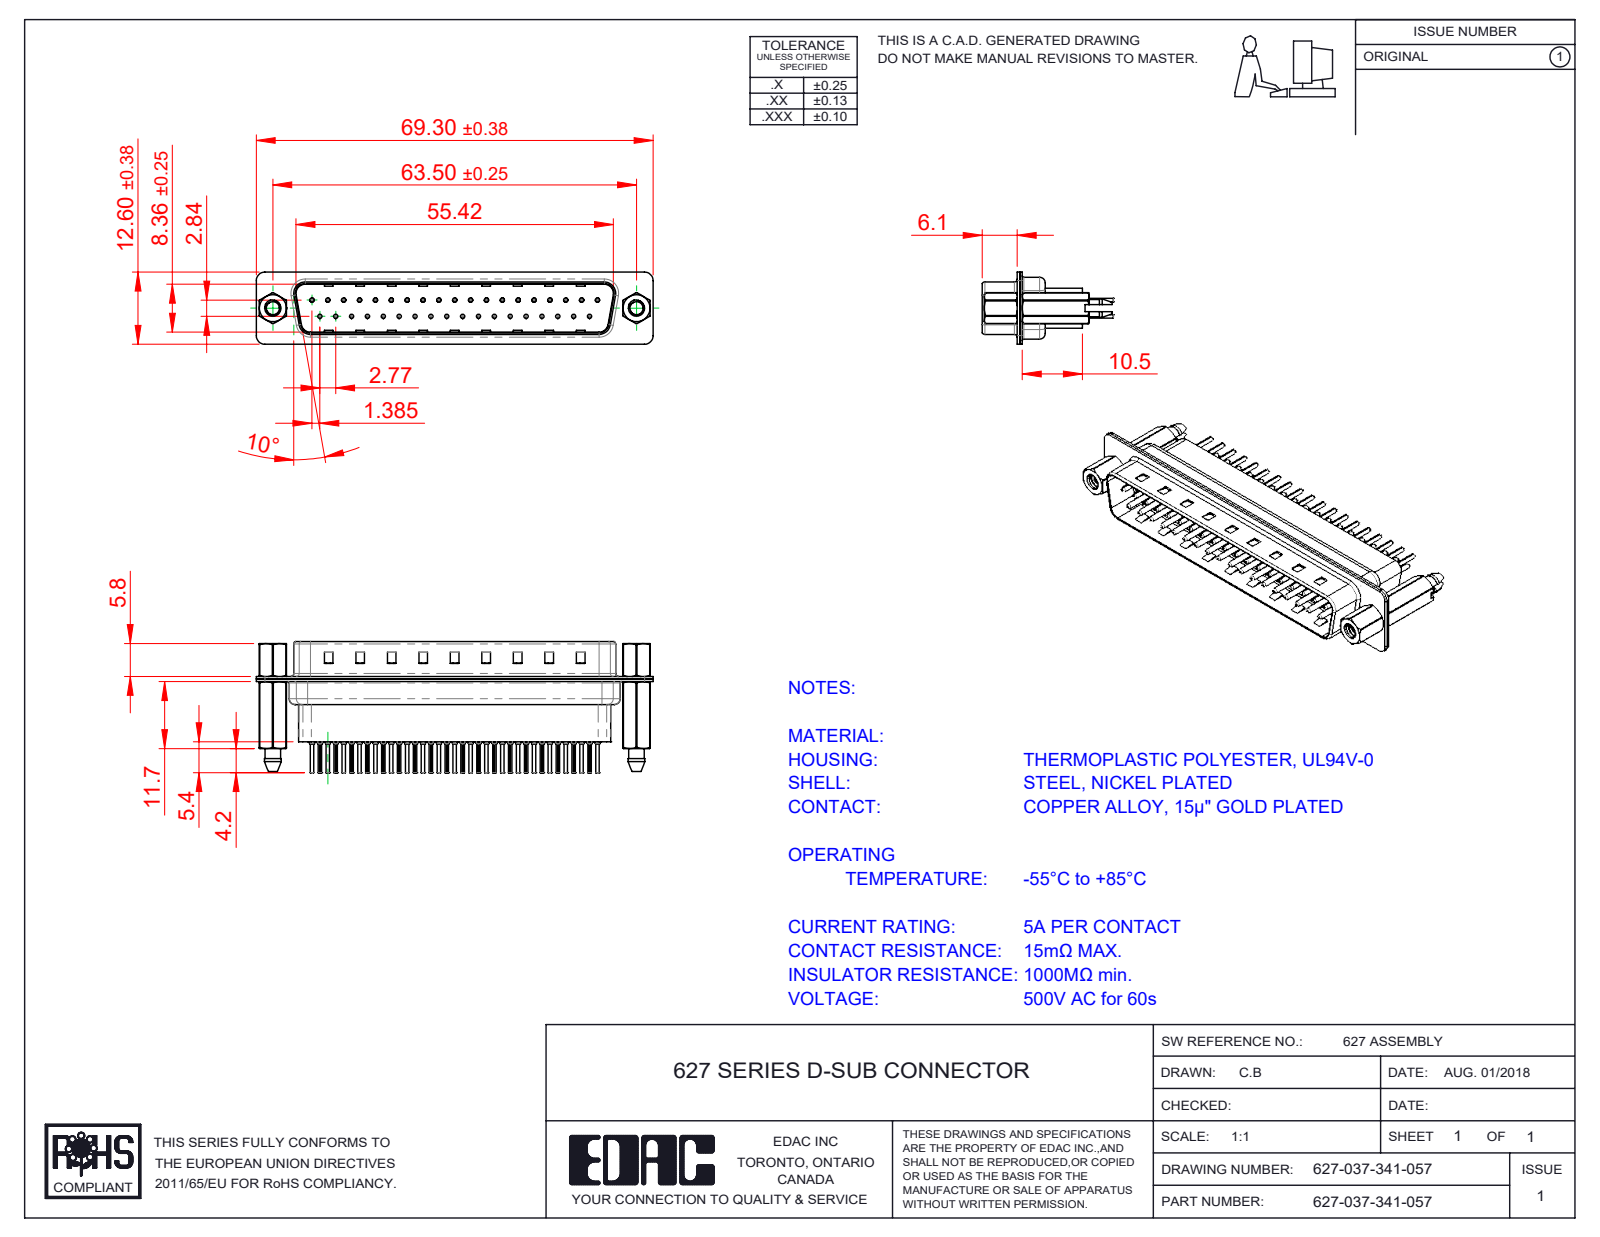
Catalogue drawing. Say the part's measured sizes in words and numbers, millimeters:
The part is named "627-037-341-057; 627 Contact Row 1_41; 627 Contact Row 2_41; 627 Shell Front_37 Contacts (+4 more)". Its 3-D file was written by "SolidWorks 2020 (CONFIG_CONTROL_DESIGN)". It is 44 solids with 4272 faces: 1145 planar, 1648 cylindrical and 1479 other. Overall it measures 69.3 by 22.8 by 12.6 millimeters. Its volume is 5 817 cubic millimeters and its surface area 14 880 square millimeters. Round holes: 37 of diameter 0.2, 37 of diameter 0.35, 37 of diameter 1.1, 37 of diameter 1.6, 2 of diameter 2.26, 2 of diameter 2.29, 2 of diameter 4, 2 of diameter 4.8. Round bosses or shafts: 37 of diameter 2, 37 of diameter 1.5, 37 of diameter 0.75, 37 of diameter 0.6, 2 of diameter 4.9, 2 of diameter 2.79. Partial cylindrical surfaces (rounded edges, fillets, slot ends): 74 of radius 0.1, 18 of radius 1.5, 12 of radius 2, 10 of radius 1.6, 8 of radius 0.5, 4 of radius 0.25, 4 of radius 0.6, 4 of radius 0.65. The main face-to-face distances are 0.4, 0.82, 9.58, 0.45, 0.68, 7.68, 1.5, 1.08, 8.08, 8.76. The hole center spacings are 3.16, 2.77, 5.54, 8.31, 5.04, 10.1, 11.08, 12.78.
